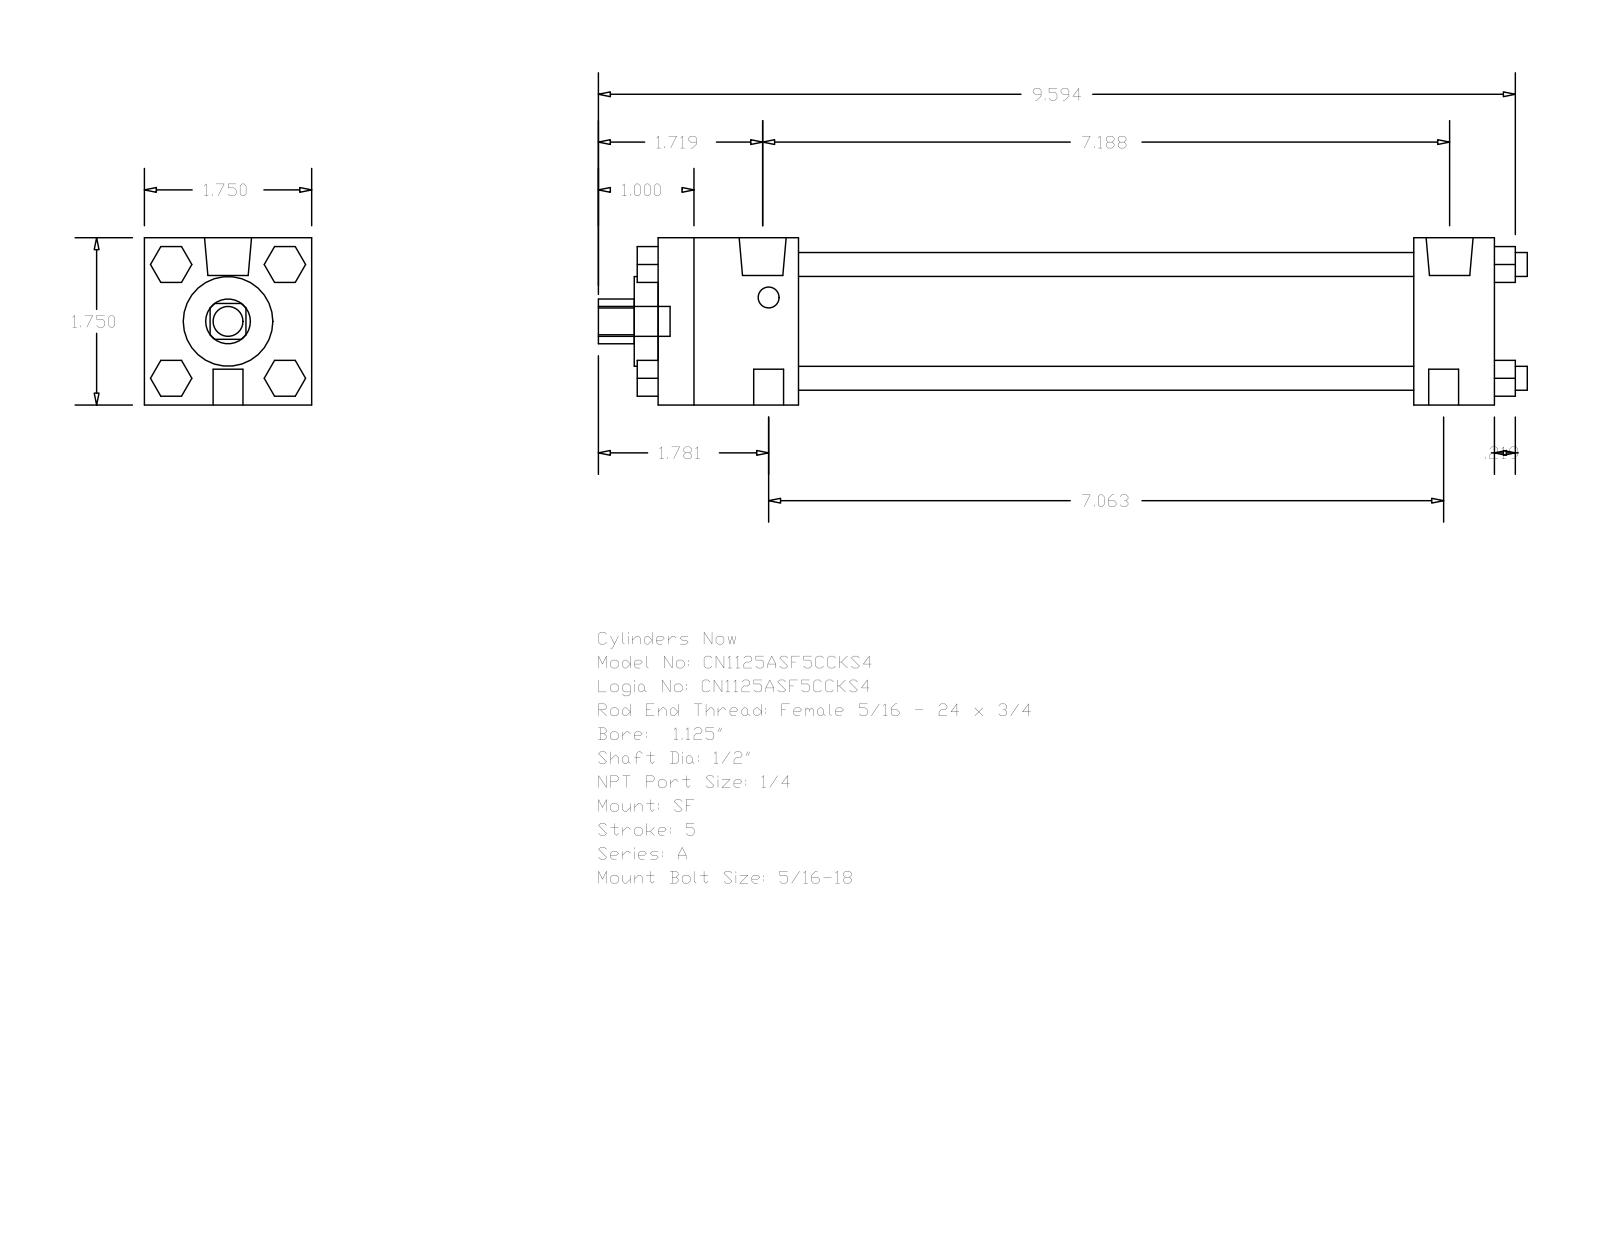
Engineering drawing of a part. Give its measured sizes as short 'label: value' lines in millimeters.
name: A_SF__0112_0.5
written by: GSSL Pune (CONFIG_CONTROL_DESIGN)
unit: mm
bodies: 0 solids, 120 faces (92 planar, 28 cylindrical, 0 other)
size: 246.86 × 44.45 × 44.45
holes: 1× ⌀12.7, 1× ⌀23.81, 1× ⌀31.88
bosses: 4× ⌀6.35, 3× ⌀7.94, 2× ⌀12.49, 2× ⌀5.56
rounds: 1× R5.94
face distances: 44.46, 222.24, 200.81, 21.43, 37.3, 163.51, 184.94, 9.53, 5.59, 9.52
